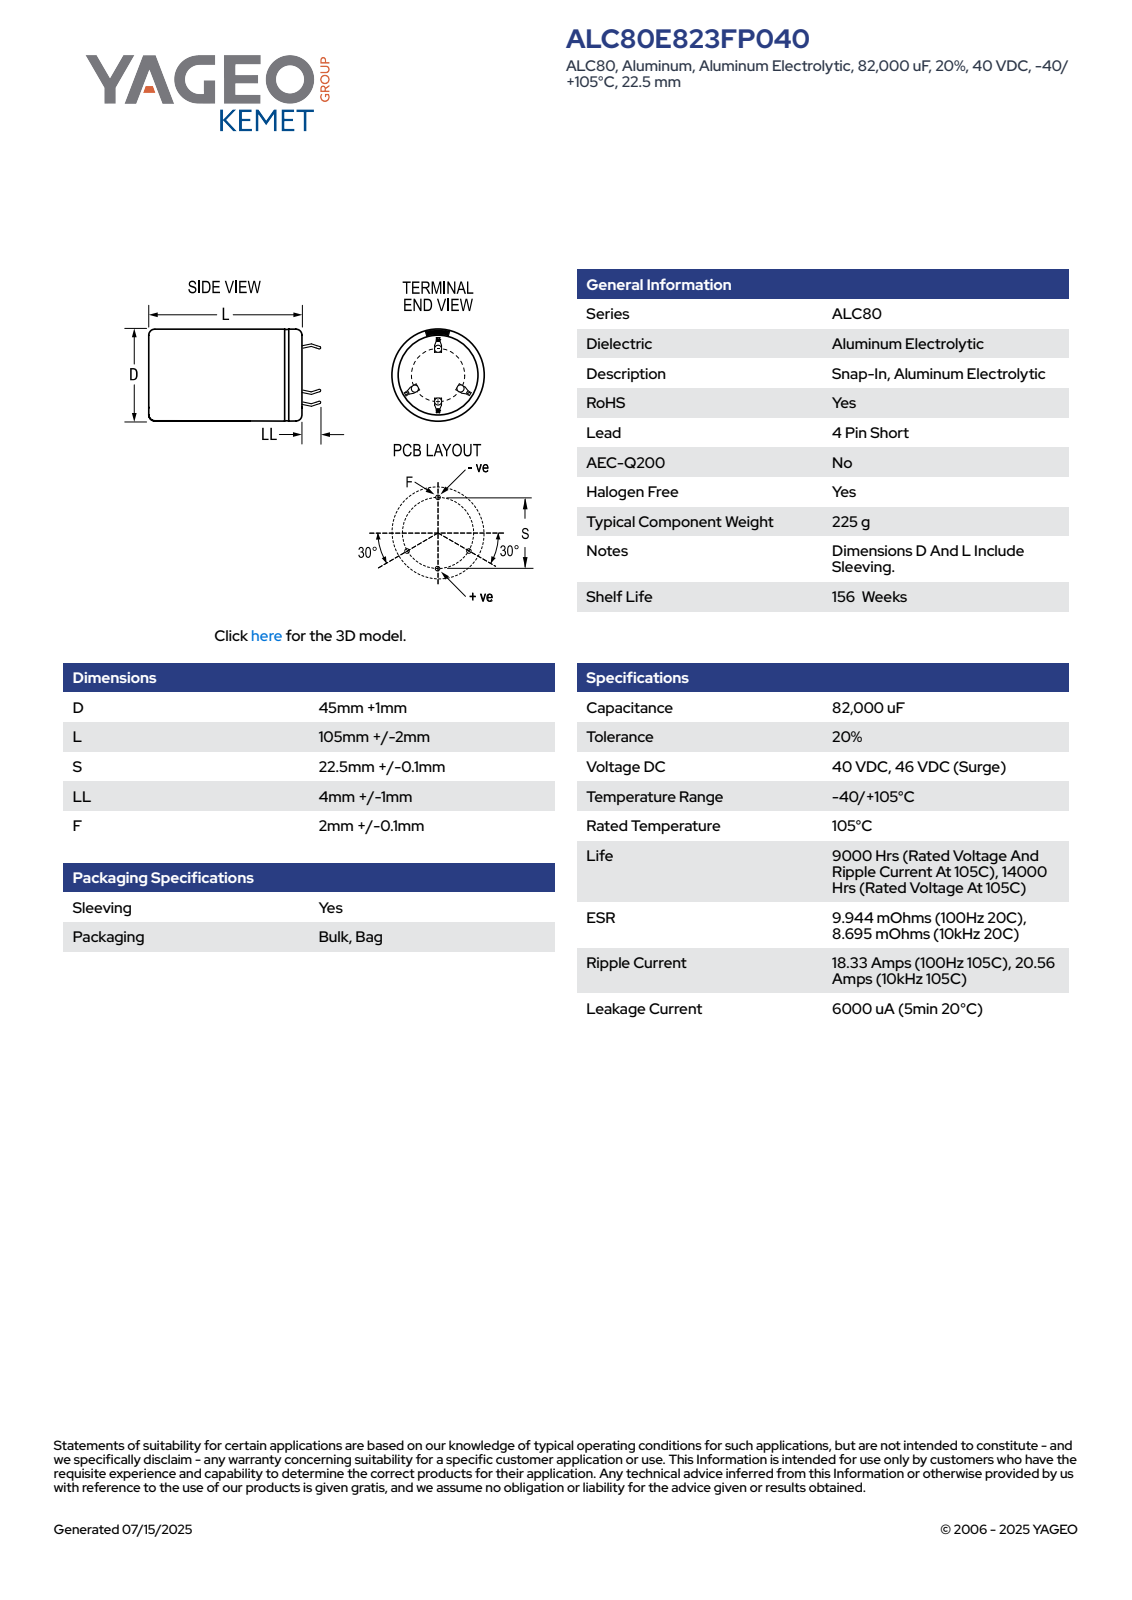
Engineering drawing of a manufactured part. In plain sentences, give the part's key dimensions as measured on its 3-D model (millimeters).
The part is named "CARS_K4P_45X105_D46L107S22.5LL5F2.1". Its 3-D file was written by "SolidWorks 2014 (AUTOMOTIVE_DESIGN)". It is 1 solid with 134 faces: 80 planar, 15 cylindrical and 39 other. Overall it measures 111.99 by 46 by 46 millimeters. Its volume is 176 721 cubic millimeters and its surface area 18 813 square millimeters. Round holes: 1 of diameter 40.7. Round bosses or shafts: 1 of diameter 46. Partial cylindrical surfaces (rounded edges, fillets, slot ends): 1 of radius 22.99. The main face-to-face distances are 106.99, 107.49, 0.5, 12.49, 0.6, 0.75, 1.35, 12.27, 12.71, 2.1.
